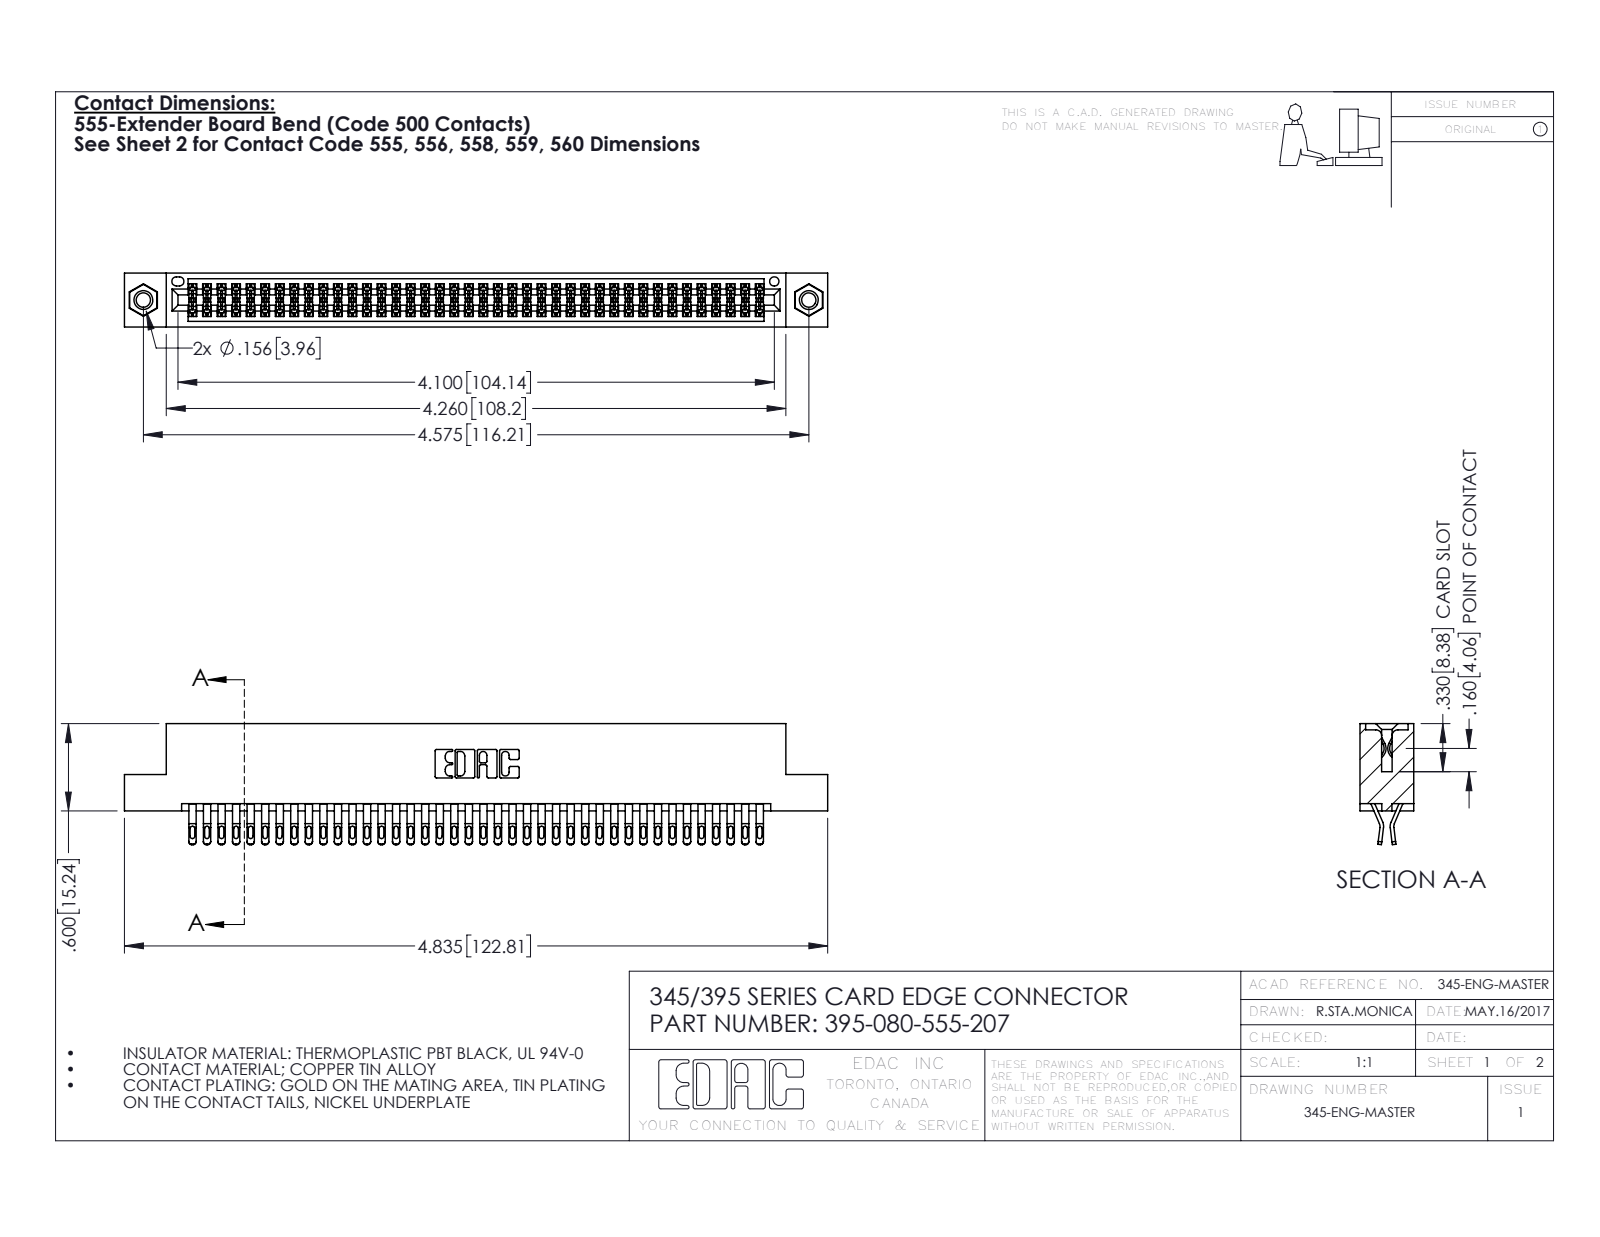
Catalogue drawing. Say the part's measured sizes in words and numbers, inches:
The part is named "345-292-001_555 Tail; 345 Part_Flush Mounting Lugs - 0.156 Dia-TI; 345-250-001_345-250-005-103; 395-080-555-207". Its 3-D file was written by "SolidWorks 2016 (CONFIG_CONTROL_DESIGN)". It is 83 solids with 4666 faces: 2592 planar, 2058 cylindrical and 16 other. Overall it measures 4.835 by 0.832 by 0.37 inches. Its volume is 0.74 cubic inches and its surface area 29.03 square inches. Round holes: 2 of diameter 0.098, 2 of diameter 0.125, 2 of diameter 0.156, 1 of diameter 0.064. Round bosses or shafts: 2 of diameter 0.155. Partial cylindrical surfaces (rounded edges, fillets, slot ends): 200 of radius 0.016, 160 of radius 0.02, 120 of radius 0.006, 22 of radius 0.01, 6 of radius 0.007, 6 of radius 0.031, 3 of radius 0.026, 2 of radius 0.01. The main face-to-face distances are 0.072, 0.298, 0.2, 0.025, 0.37, 0.098, 0.272, 0.225, 0.175, 0.149. The hole center spacings are 0.27, 4.339, 4.575.
